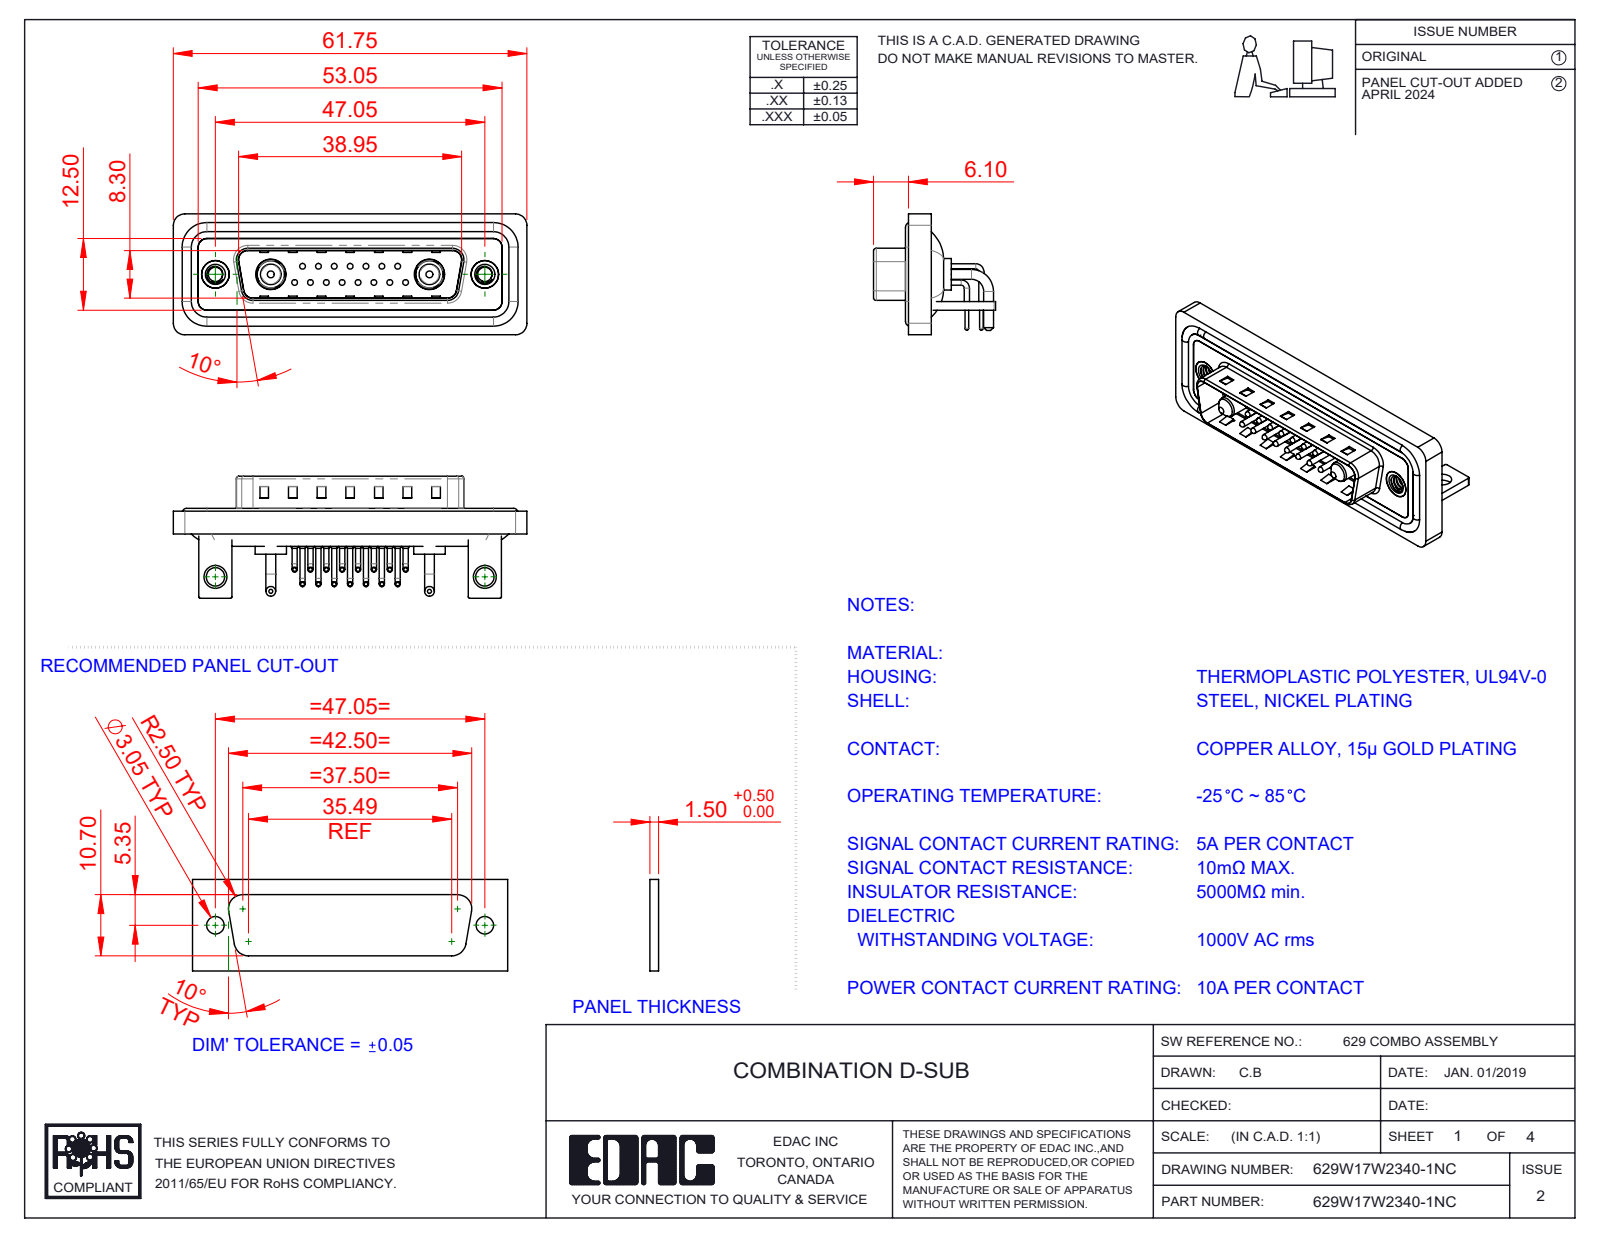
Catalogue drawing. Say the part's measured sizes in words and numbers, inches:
The part is named "629Combo Threaded Rivet_B; Power Pin_10A RA; 629Combo Waterproof Housing_25 Contacts; 629Combo Shell Rear_25 Contacts (+6 more)". Its 3-D file was written by "SolidWorks 2023 (CONFIG_CONTROL_DESIGN)". It is 28 solids with 2257 faces: 1209 planar, 788 cylindrical and 260 other. Overall it measures 2.431 by 0.839 by 0.831 inches. Its volume is 0.468 cubic inches and its surface area 20.28 square inches. Round holes: 15 of diameter 0.03, 15 of diameter 0.063, 15 of diameter 0.079, 2 of diameter 0.098, 2 of diameter 0.126, 2 of diameter 0.157, 2 of diameter 0.189, 2 of diameter 0.191, 2 of diameter 0.197, 2 of diameter 0.209. Round bosses or shafts: 30 of diameter 0.035, 15 of diameter 0.059, 15 of diameter 0.039, 15 of diameter 0.026, 4 of diameter 0.067, 4 of diameter 0.063, 2 of diameter 0.217, 2 of diameter 0.205. Partial cylindrical surfaces (rounded edges, fillets, slot ends): 19 of radius 0.079, 18 of radius 0.059, 16 of radius 0.01, 15 of radius 0.04, 9 of radius 0.02, 8 of radius 0.063, 4 of radius 0.024, 4 of radius 0.026. The main face-to-face distances are 0.016, 0.031, 0.059, 0.083, 0.114, 0.043, 0.161, 0.063, 0.177, 0.146. The hole center spacings are 0.124, 0.109, 0.218, 0.327, 0.198, 0.295, 0.436, 0.198.
